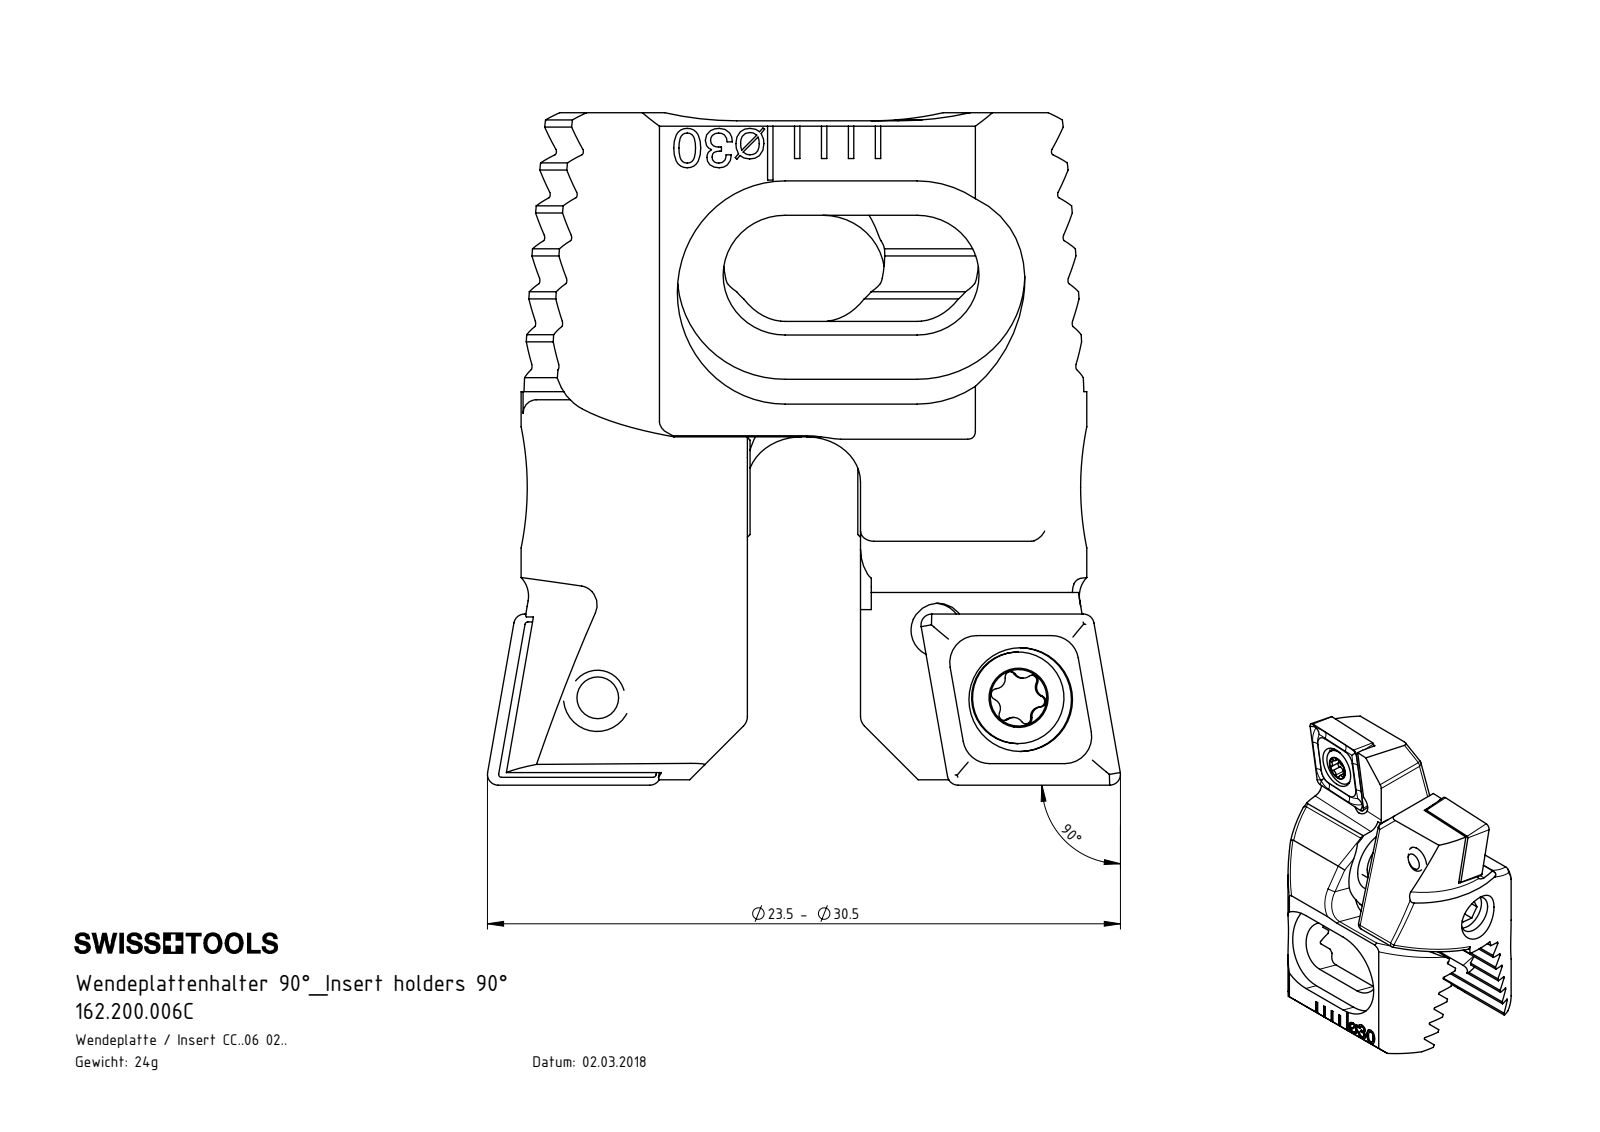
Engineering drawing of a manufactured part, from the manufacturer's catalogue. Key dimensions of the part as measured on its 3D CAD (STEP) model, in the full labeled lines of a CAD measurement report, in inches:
Part name (STEP PRODUCT): 162.200.006C; CCMT060204; Z20-xxx.001.015_D; Z20-ER3.001.007_A (+1 more)
STEP written by: SolidWorks 2017 (CONFIG_CONTROL_DESIGN)
Units: inches
Bodies: 8 solids, 606 faces (262 planar, 134 cylindrical, 210 other)
Overall size (bounding box): 0.982 × 0.925 × 0.638
Volume: 0.181 in³ · Surface area: 5.29 in²
Round holes (diameter × count): ⌀0.063 ×2, ⌀0.079 ×2, ⌀0.081 ×2, ⌀0.11 ×2, ⌀0.152 ×2, ⌀0.138 ×1, ⌀0.358 ×1
Round bosses / shafts (diameter × count): ⌀0.134 ×2, ⌀0.098 ×2, ⌀0.157 ×1
Partial cylindrical surfaces — rounded edges, fillets, slot ends (radius × count): R0.02 ×16, R0.005 ×12, R0.008 ×12, R0.014 ×10, R0.039 ×4, R0.079 ×4, R0.091 ×4, R0.157 ×4
Main face-to-face distances: 0.056, 0.113, 0.169, 0.149, 0.016, 0.181, 0.225, 0.225, 0.117, 0.266
Hole centre spacings: 0.154, 0.158, 0.217, 0.518, 0.521, 0.629, 0.39, 0.418
